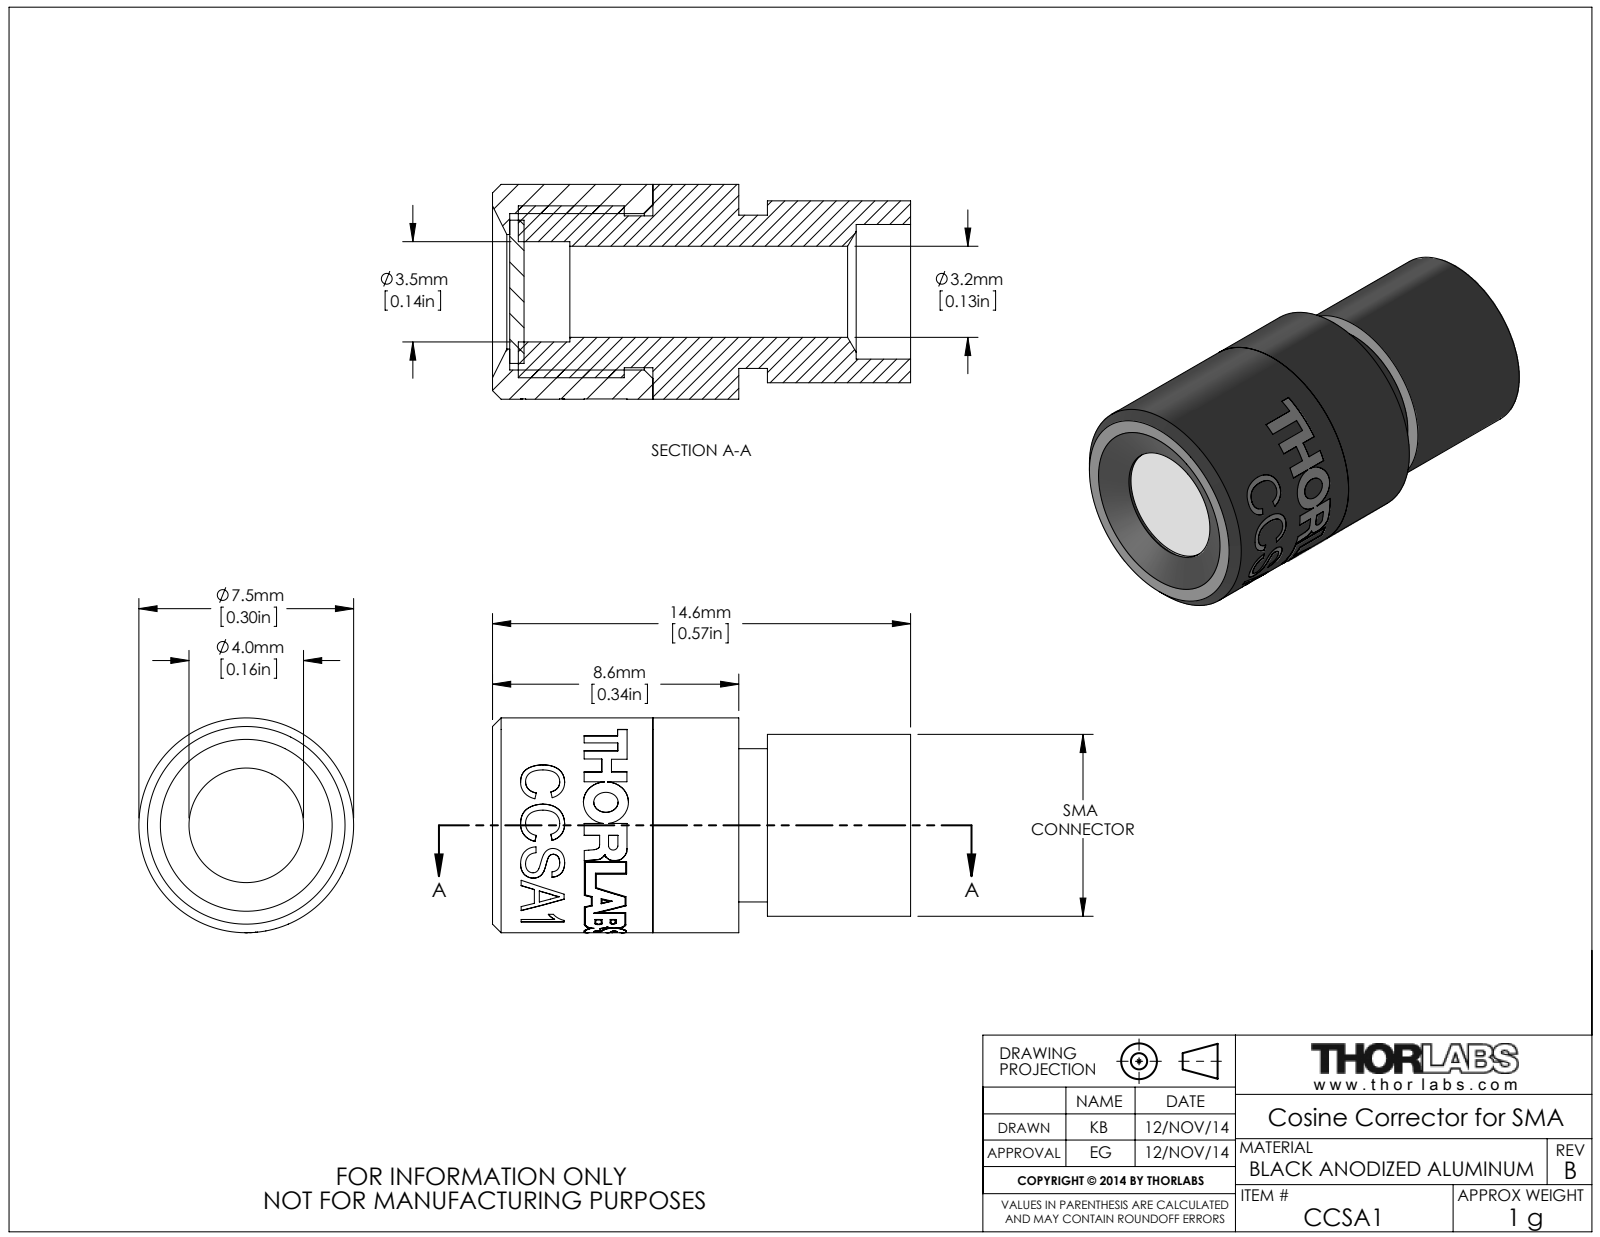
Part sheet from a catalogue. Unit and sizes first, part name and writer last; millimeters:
Units: millimetres
Overall size (bounding box): 14.6 × 7.5 × 7.5
Round holes (diameter × count): ⌀3.18 ×1, ⌀3.5 ×1, ⌀4 ×1, ⌀4.7 ×1, ⌀5.46 ×1
Round bosses / shafts (diameter × count): ⌀7.5 ×1, ⌀6.35 ×1, ⌀6 ×1, ⌀5.35 ×1, ⌀5.3 ×1, ⌀5 ×1
Partial cylindrical surfaces — rounded edges, fillets, slot ends (radius × count): R3.74 ×1
Main face-to-face distances: 5, 9, 8, 3, 4, 0.5, 4.5, 7.5, 4.7, 7.7
Volume: 437 mm³ · Surface area: 848 mm²
Bodies: 3 solids, 467 faces (52 planar, 30 cylindrical, 385 other)
Part name (STEP PRODUCT): CCSA1-inkl Spektralon-12.11.2014
STEP written by: SolidWorks 2014 (AUTOMOTIVE_DESIGN)
